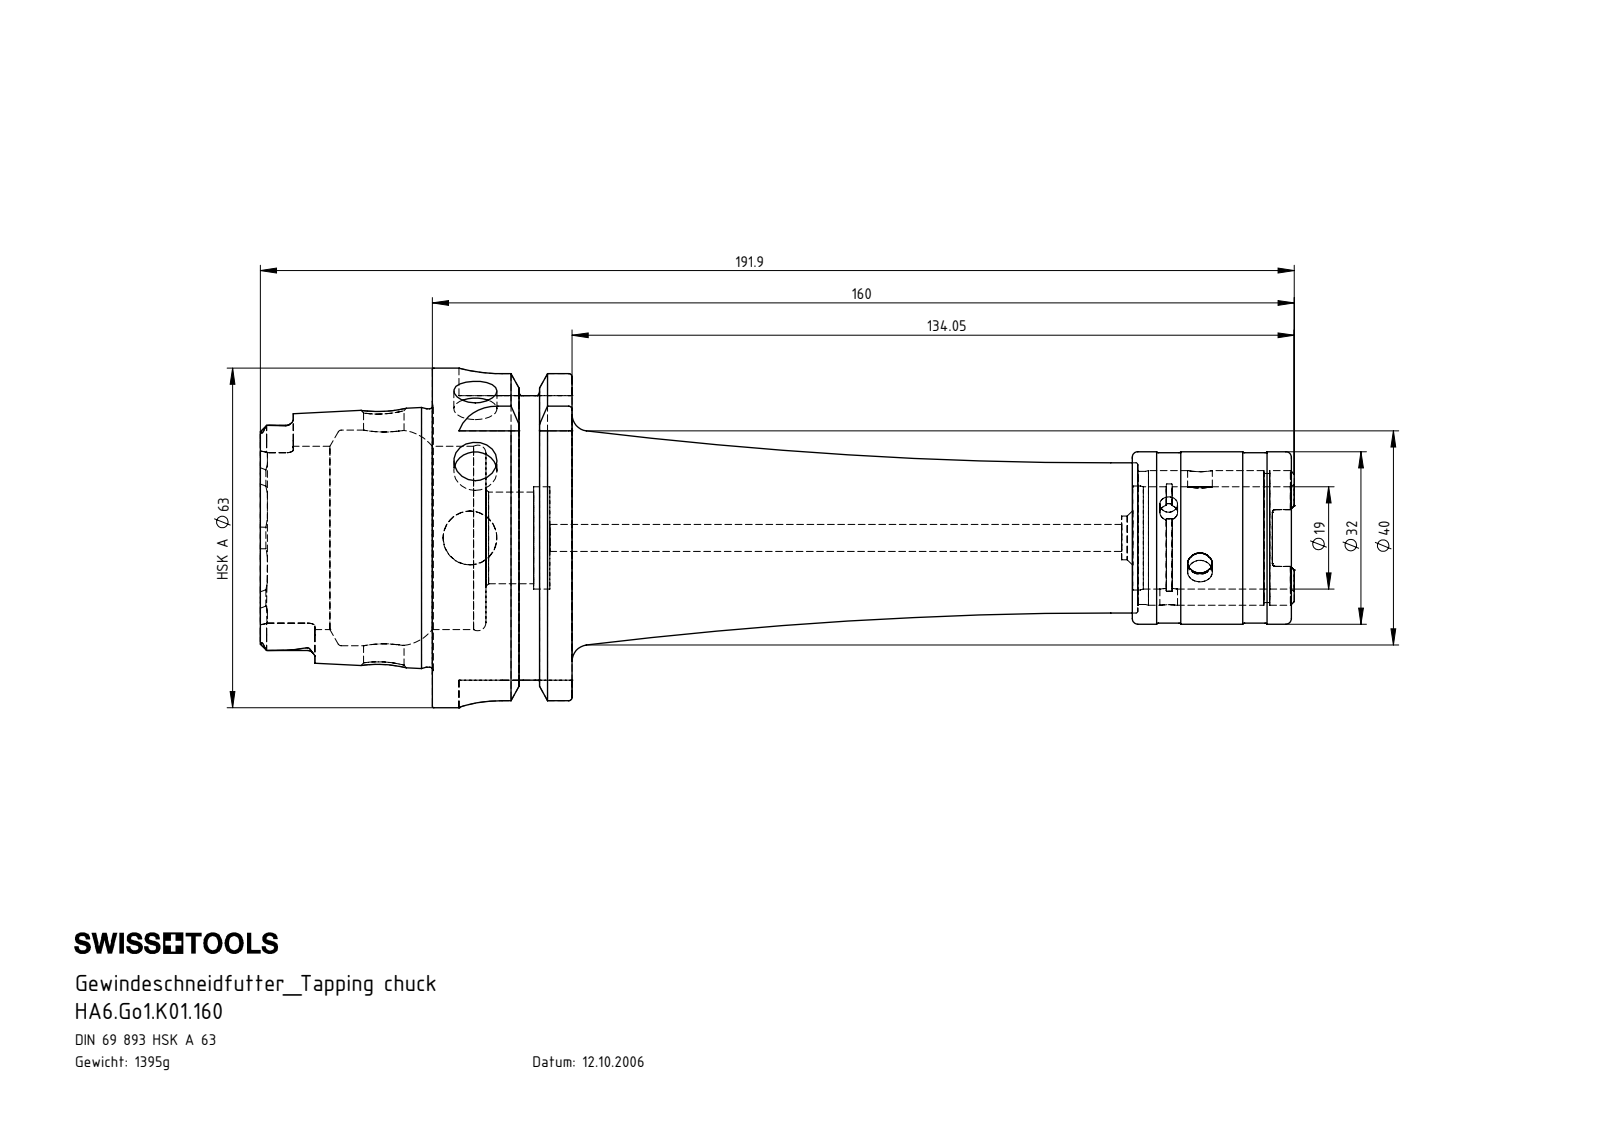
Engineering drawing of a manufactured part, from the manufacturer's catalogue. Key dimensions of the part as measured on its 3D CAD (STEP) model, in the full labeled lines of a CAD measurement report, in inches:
Part name (STEP PRODUCT): HA6.Go1.K01.160; Einbausatz Go1_gespannt; Kugel Go1; Hülse Go1 (+6 more)
STEP written by: SolidWorks 2011 (AUTOMOTIVE_DESIGN)
Units: inches
Bodies: 10 solids, 386 faces (89 planar, 119 cylindrical, 178 other)
Overall size (bounding box): 7.555 × 2.48 × 2.48
Volume: 10.83 in³ · Surface area: 73.91 in²
Round holes (diameter × count): ⌀0.13 ×3, ⌀0.181 ×3, ⌀0.315 ×3, ⌀0.079 ×1, ⌀0.197 ×1, ⌀0.295 ×1, ⌀0.319 ×1, ⌀0.394 ×1, ⌀0.669 ×1, ⌀0.748 ×1, ⌀0.76 ×1, ⌀0.789 ×1
Round bosses / shafts (diameter × count): ⌀2.48 ×1, ⌀2.163 ×1, ⌀1.887 ×1, ⌀1.26 ×1, ⌀1.244 ×1, ⌀1.096 ×1, ⌀0.984 ×1, ⌀0.972 ×1
Partial cylindrical surfaces — rounded edges, fillets, slot ends (radius × count): R0.055 ×6, R0.113 ×4, R0.315 ×4, R0.085 ×3, R0.02 ×2
Main face-to-face distances: 1.022, 0.63, 0.392, 1.256, 1.648, 2.278, 0.858, 2.079, 0.467, 2.114
Hole centre spacings: 0.228, 5.736, 5.965
